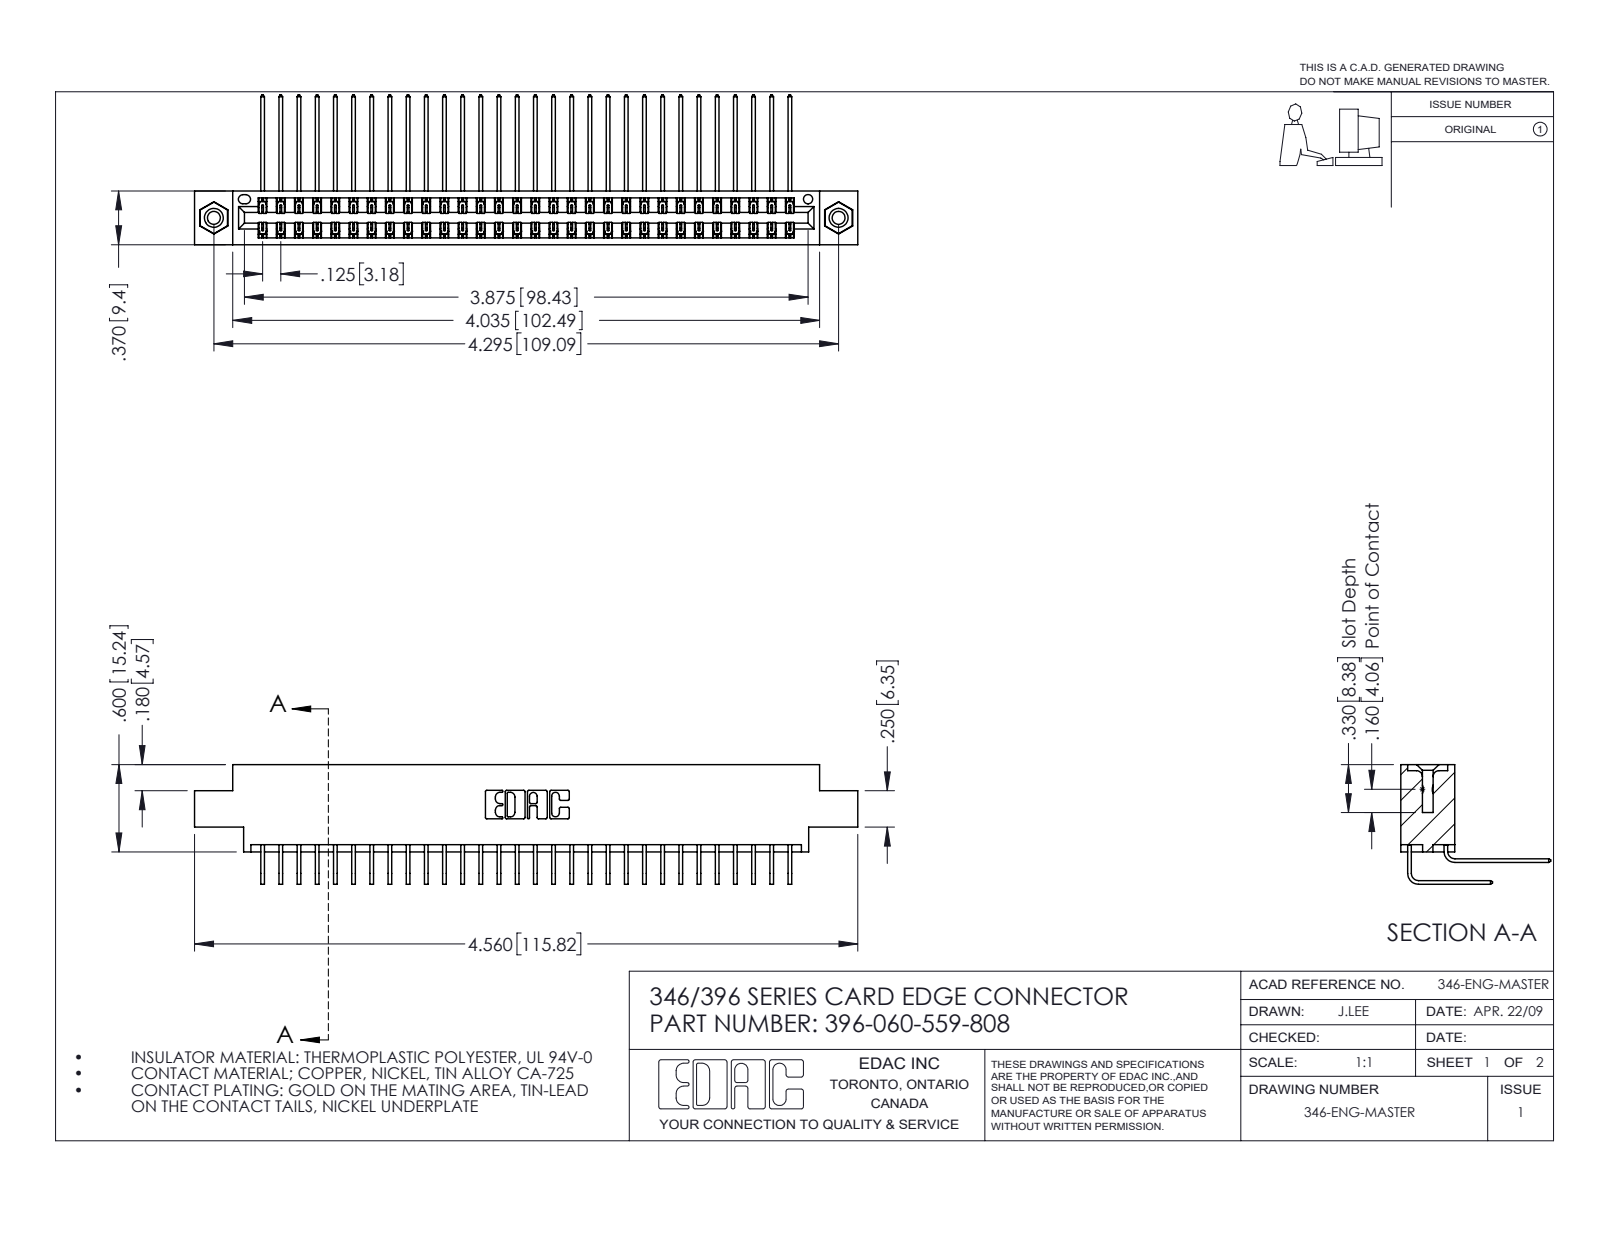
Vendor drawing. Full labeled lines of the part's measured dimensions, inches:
Part name (STEP PRODUCT): 345-250-001_345-250-003-102; 396-060-559-808; 345-292-001_558 559 Tail - 1; 346 Part_0.170 Offset - 0.156 Dia-TI (+1 more)
STEP written by: SolidWorks 2016 (CONFIG_CONTROL_DESIGN)
Units: inches
Bodies: 63 solids, 3426 faces (2332 planar, 1078 cylindrical, 16 other)
Overall size (bounding box): 4.56 × 1.03 × 0.823
Volume: 0.695 in³ · Surface area: 26.85 in²
Round holes (diameter × count): ⌀0.089 ×2, ⌀0.125 ×2, ⌀0.156 ×2, ⌀0.064 ×1
Round bosses / shafts (diameter × count): ⌀0.155 ×2
Partial cylindrical surfaces — rounded edges, fillets, slot ends (radius × count): R0.006 ×90, R0.01 ×22, R0.007 ×6, R0.031 ×6, R0.026 ×3, R0.014 ×2, R0.022 ×2, R0.024 ×2
Main face-to-face distances: 0.048, 0.322, 0.025, 0.37, 0.25, 0.072, 0.298, 0.275, 0.222, 0.148
Hole centre spacings: 0.246, 4.087, 4.295
